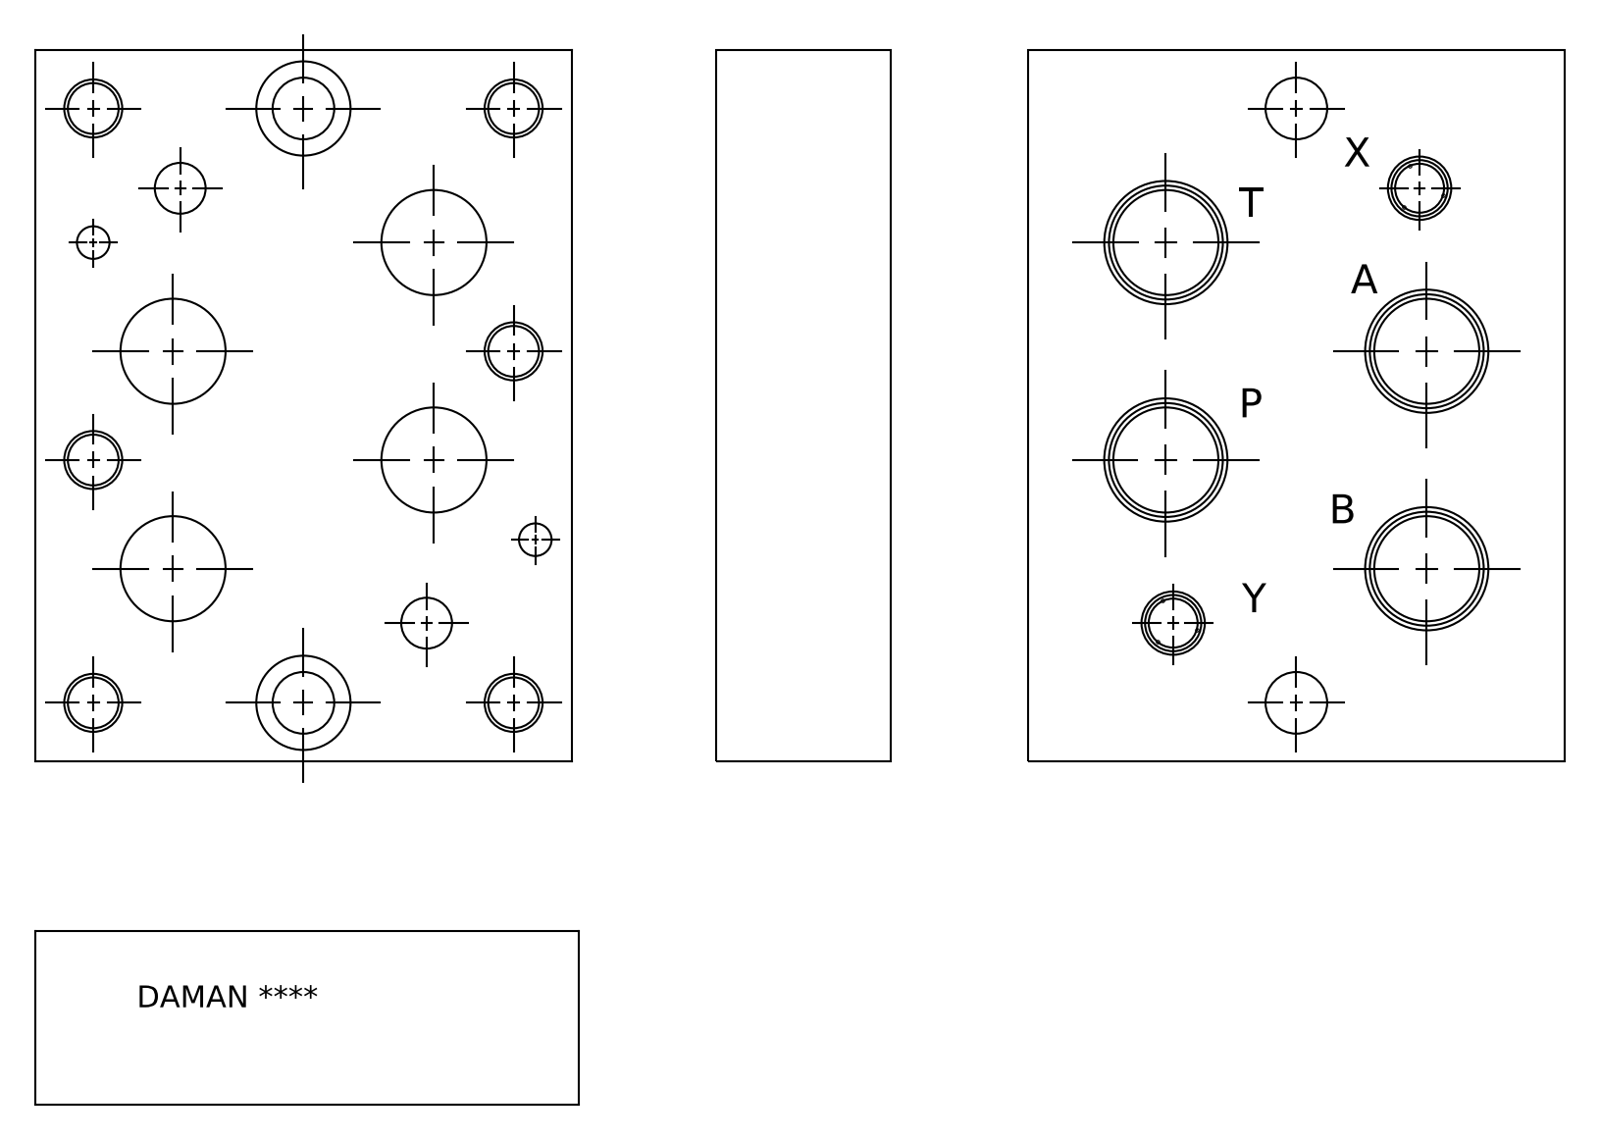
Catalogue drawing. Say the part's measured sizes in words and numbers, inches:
The part is named "Part_AD08SPB12P_3D". Its 3-D file was written by "Autodesk Inventor 2019 (AUTOMOTIVE_DESIGN)". It is 1 solid with 478 faces: 313 planar, 30 cylindrical and 135 other. Overall it measures 6.125 by 4.625 by 1.5 inches. Its volume is 34.9 cubic inches and its surface area 124.6 square inches. Round holes: 8 of diameter 0.422, 6 of diameter 0.5, 4 of diameter 1.06, 3 of diameter 0.906, 2 of diameter 0.281, 2 of diameter 0.531, 2 of diameter 0.546, 2 of diameter 0.812, 1 of diameter 0.906. The main face-to-face distances are 1.5, 4.625, 6.125, 0.75, 0.624, 0.876, 0.126, 0.44, 0.184, 0.31. The hole center spacings are 1.163, 1.814, 1.875, 2.094, 2.204, 2.438, 2.956, 3.031.
